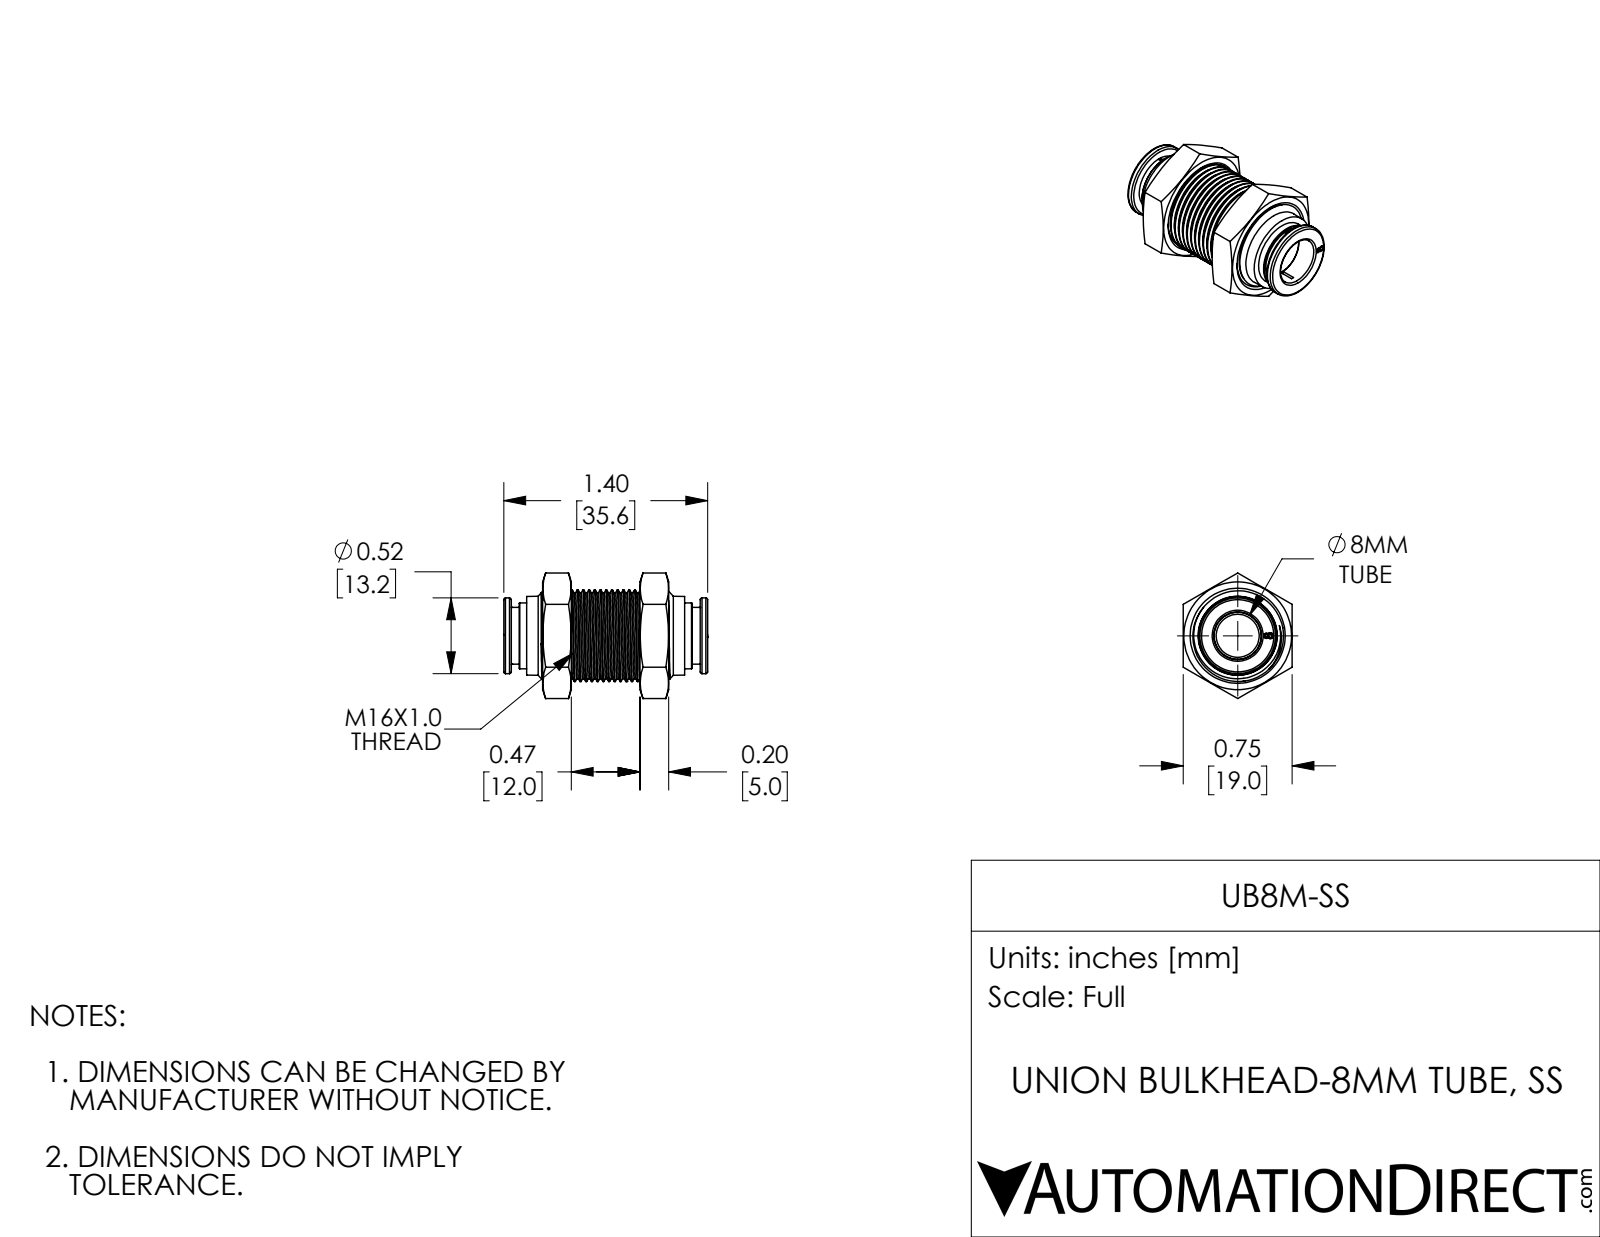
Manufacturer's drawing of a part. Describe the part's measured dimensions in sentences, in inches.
The part is named "UB8M-SS". Its 3-D file was written by "SolidWorks 2017 (AUTOMOTIVE_DESIGN)". It is 1 solid with 216 faces: 46 planar, 90 cylindrical and 80 other. Overall it measures 1.402 by 0.864 by 0.748 inches. Its volume is 0.313 cubic inches and its surface area 6.691 square inches. Round holes: 1 of diameter 0.295, 1 of diameter 0.323, 1 of diameter 0.327, 1 of diameter 0.394. Round bosses or shafts: 1 of diameter 0.63, 1 of diameter 0.591, 1 of diameter 0.52, 1 of diameter 0.453, 1 of diameter 0.39. The main face-to-face distances are 0.748, 0.669, 0.268, 0.465, 0.937, 1.134, 0.197, 0.051, 0.106, 1.244.
